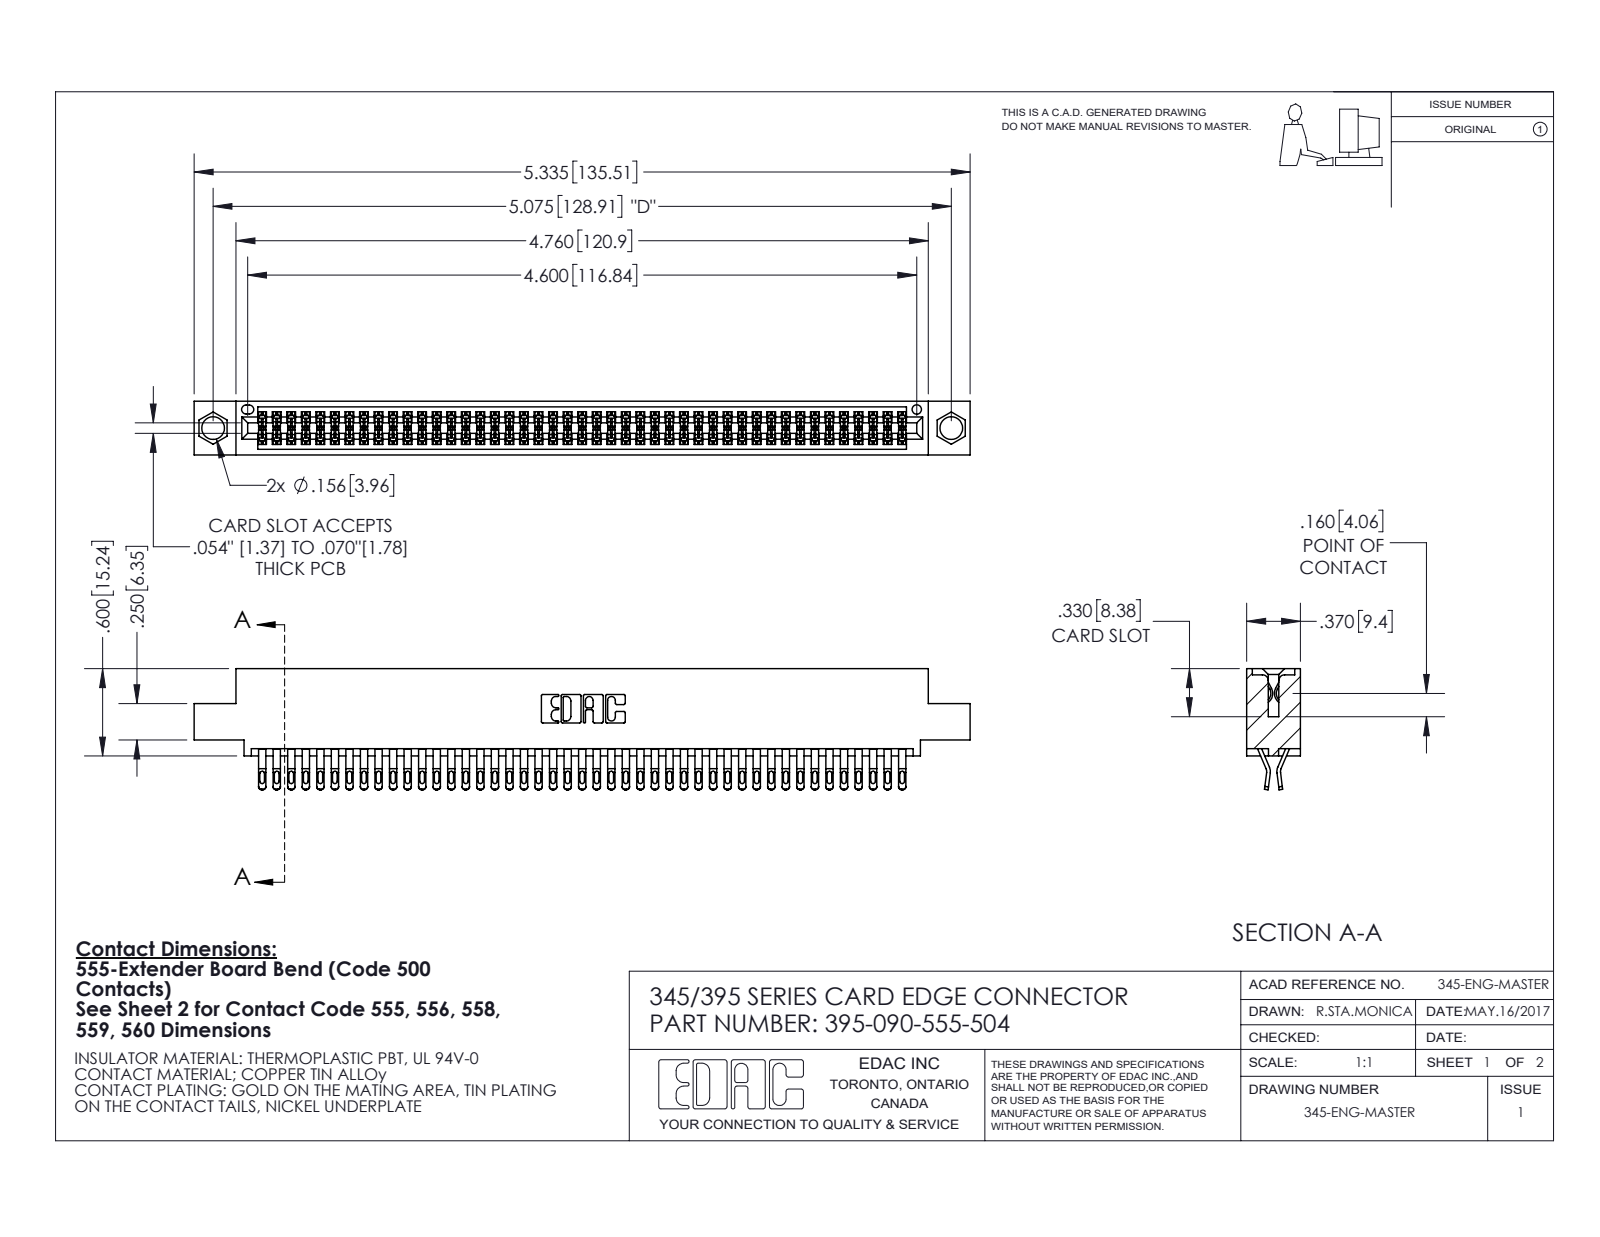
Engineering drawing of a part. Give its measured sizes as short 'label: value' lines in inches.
name: 345-292-001_555 Tail; 345 Part_0.110 Offset - 0.156 Dia-TI; 395-090-555-504
written by: SolidWorks 2020 (CONFIG_CONTROL_DESIGN)
unit: in
bodies: 91 solids, 5184 faces (2888 planar, 2296 cylindrical, 0 other)
size: 5.335 × 0.832 × 0.37
volume: 0.81 in³; area: 31.82 in²
holes: 2× ⌀0.156, 1× ⌀0.064
rounds: 225× R0.016, 180× R0.006, 180× R0.02, 22× R0.01, 6× R0.007, 6× R0.031, 3× R0.026, 2× R0.01
face distances: 0.298, 0.072, 0.025, 0.37, 0.2, 0.098, 0.272, 0.225, 0.175, 0.149
hole spacings: 0.27, 4.839, 5.075
